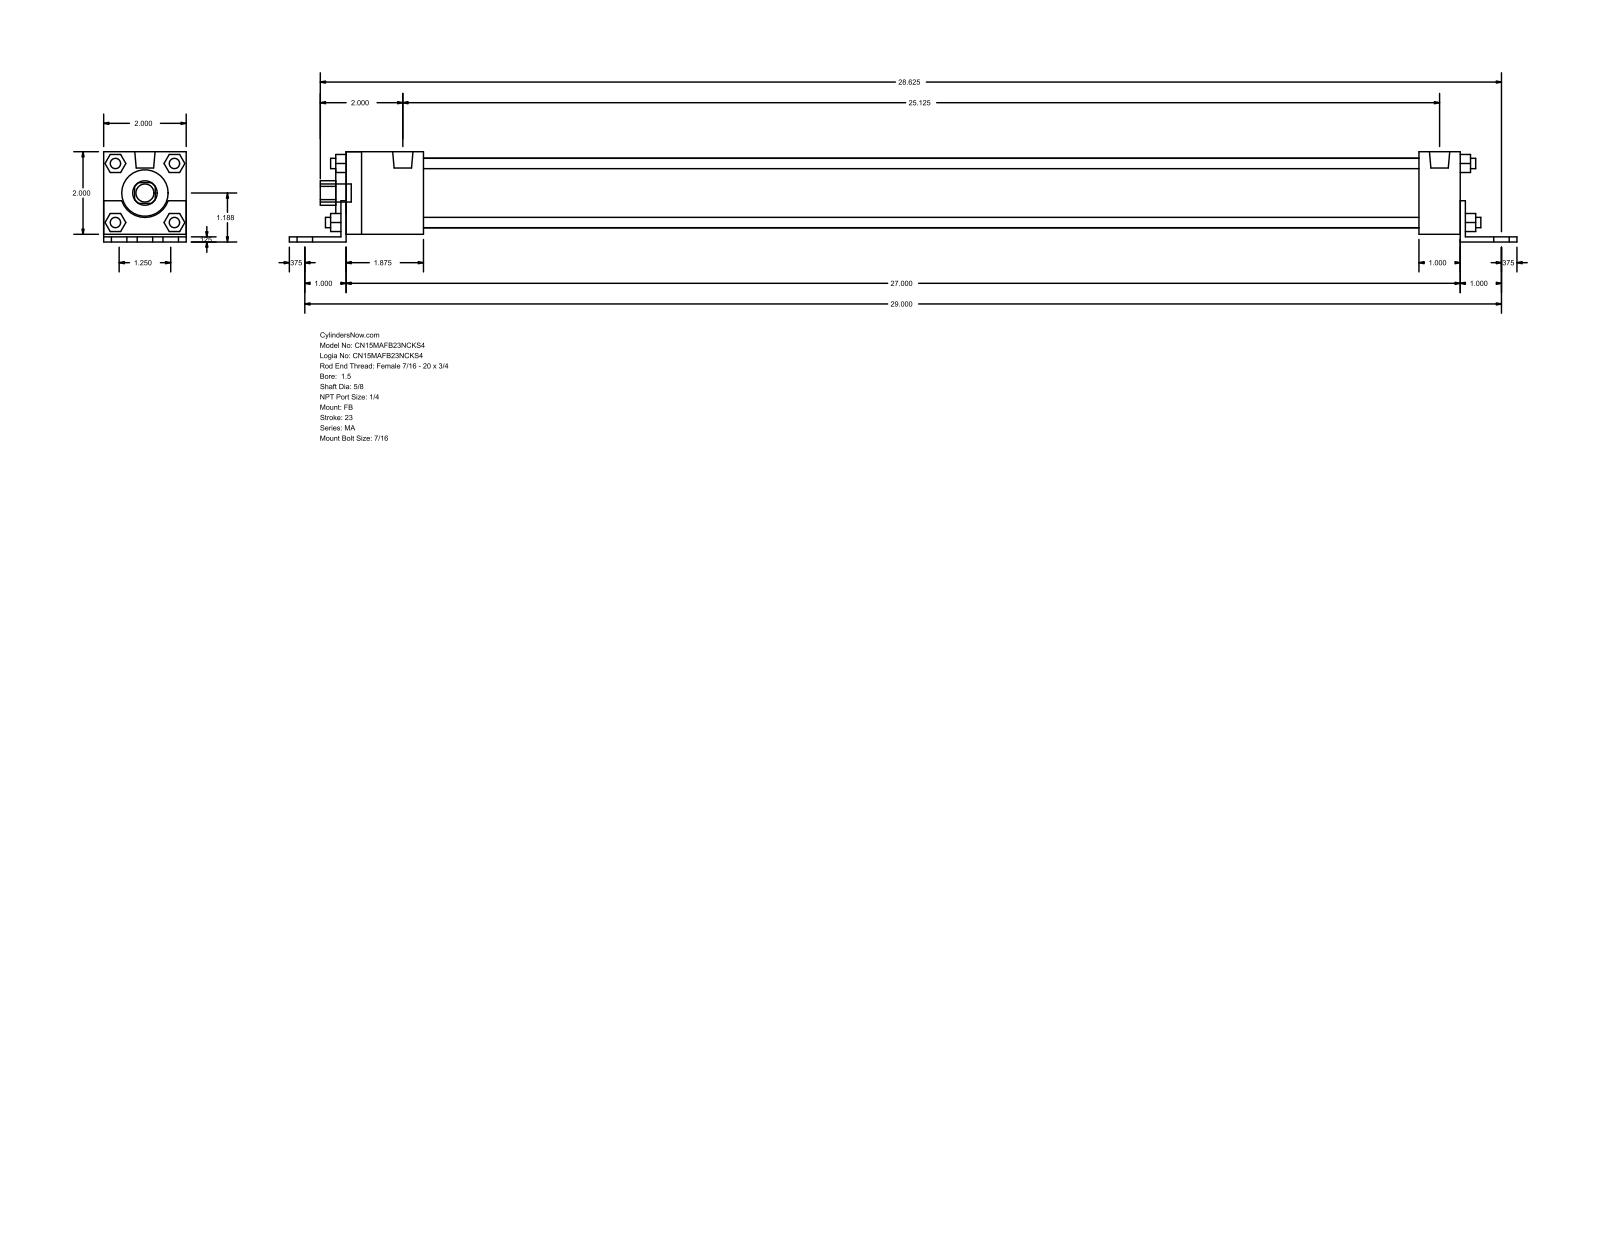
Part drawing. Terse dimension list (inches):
name: MA_FB__0150_0.625
written by: GSSL Pune (CONFIG_CONTROL_DESIGN)
unit: in
bodies: 0 solids, 140 faces (105 planar, 35 cylindrical, 0 other)
size: 29.75 × 2.187 × 2
holes: 1× ⌀0.625, 1× ⌀1.125, 1× ⌀1.69
bosses: 7× ⌀0.437, 4× ⌀0.313, 4× ⌀0.25, 2× ⌀0.492
rounds: 1× R0.297, 1× R0.593
face distances: 2, 0.125, 0.187, 2.187, 0.063, 2.063, 0.125, 27.125, 1, 27.375
